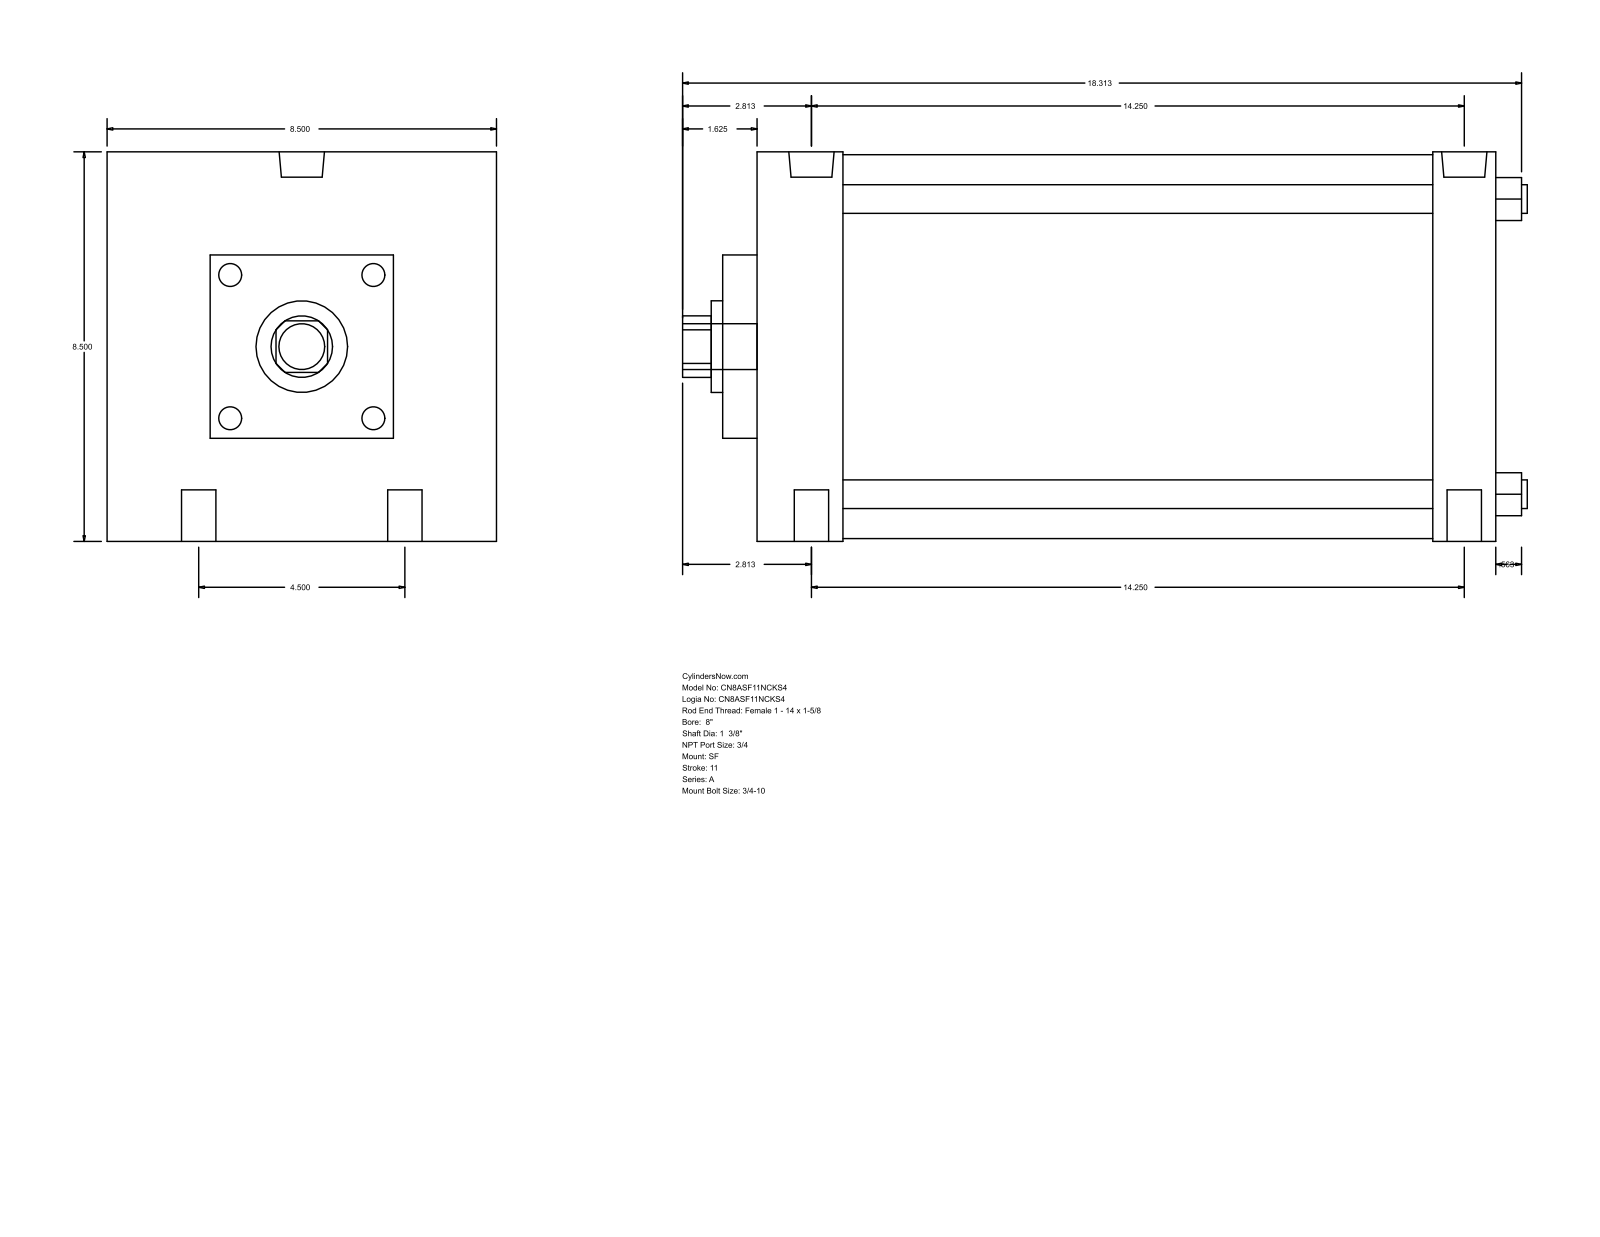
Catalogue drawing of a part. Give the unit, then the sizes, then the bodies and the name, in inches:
Units: inches
Overall size (bounding box): 18.437 × 8.5 × 8.5
Round holes (diameter × count): ⌀0.75 ×4, ⌀0.594 ×2, ⌀0.989 ×2, ⌀1.375 ×1, ⌀2 ×1
Round bosses / shafts (diameter × count): ⌀0.625 ×4, ⌀8.375 ×1, ⌀1 ×1
Partial cylindrical surfaces — rounded edges, fillets, slot ends (radius × count): R0.672 ×1
Main face-to-face distances: 16.125, 8.5, 1.875, 14.75, 12.875, 14.25, 1.375, 0.75, 2.625, 15.5
Hole centre spacings: 2.25, 14.426, 14.25, 4.5, 14.944, 13.75
Bodies: 0 solids, 93 faces (67 planar, 26 cylindrical, 0 other)
Part name (STEP PRODUCT): A_SF__0800_1.375
STEP written by: GSSL Pune (CONFIG_CONTROL_DESIGN)
